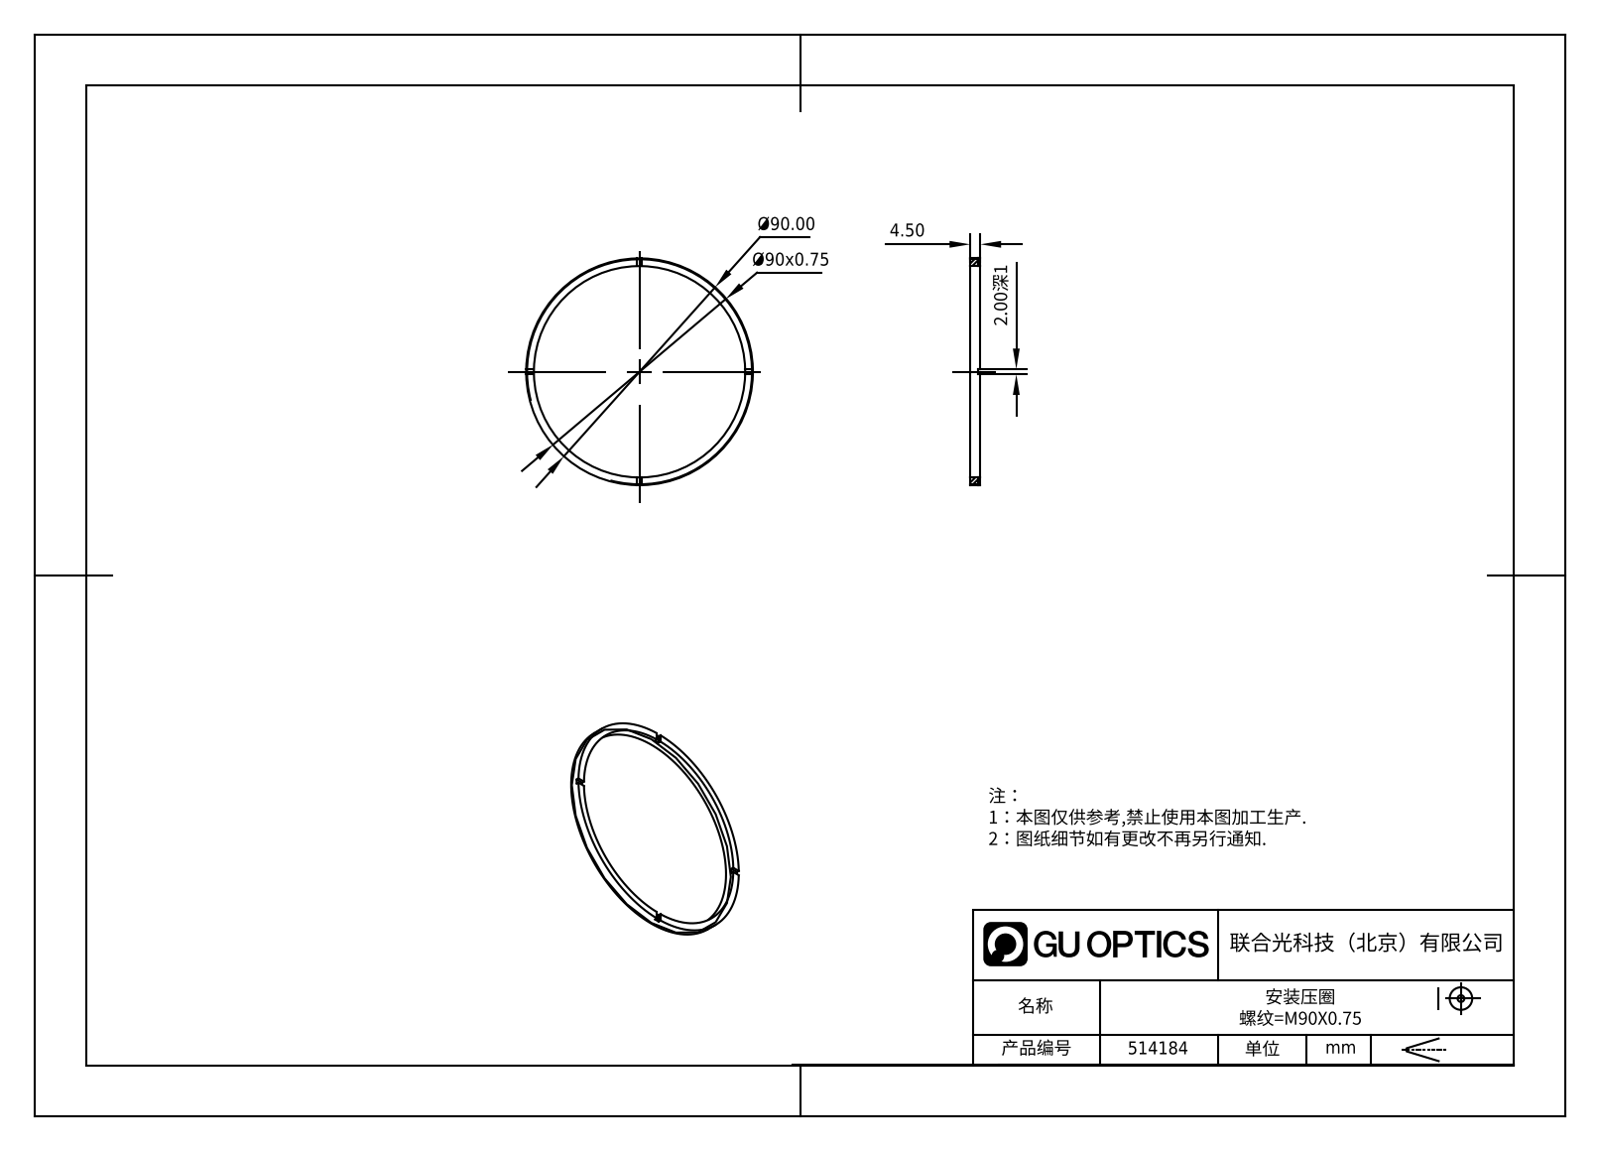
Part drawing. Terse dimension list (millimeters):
name: 514184
written by: SolidWorks 2020 (CONFIG_CONTROL_DESIGN)
unit: mm
bodies: 1 solid, 21 faces (17 planar, 4 cylindrical, 0 other)
size: 90 × 90 × 4.5
volume: 4 252 mm³; area: 4 360 mm²
holes: 1× ⌀83
bosses: 1× ⌀90
face distances: 4.5, 3.5, 1, 2
